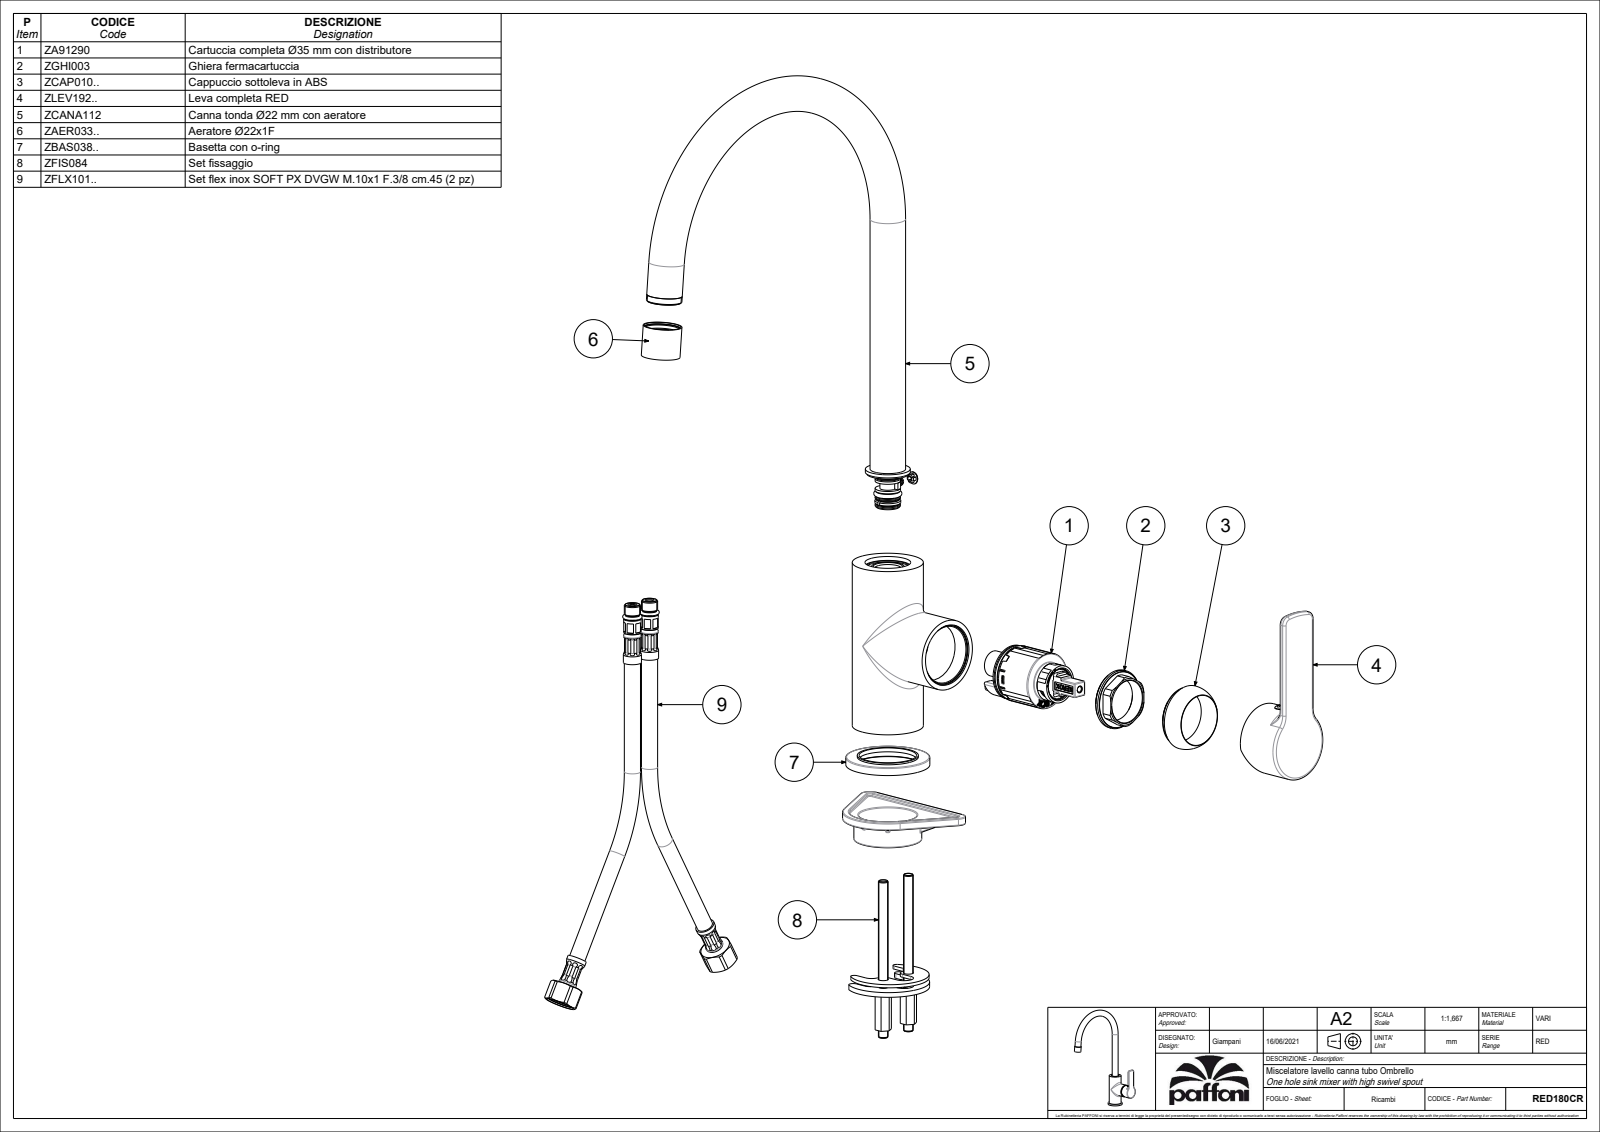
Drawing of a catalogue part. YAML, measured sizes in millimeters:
part_name: "RED180CR"
step_written_by: "CREO PARAMETRIC BY PTC INC, 2020044 (CONFIG_CONTROL_DESIGN)"
units: millimeters
bodies: {solids: 4, faces: 3570, planar: 2541, cylindrical: 604, other: 425}
overall_size: [377.3, 234.97, 111.23]
volume: 223151
surface_area: 146333
round_holes:
  - {diameter: 5.5, count: 3}
  - {diameter: 3, count: 2}
  - {diameter: 4, count: 2}
  - {diameter: 6, count: 2}
  - {diameter: 8, count: 2}
  - {diameter: 9, count: 2}
  - {diameter: 11, count: 2}
  - {diameter: 16, count: 2}
  - {diameter: 17, count: 2}
  - {diameter: 19.6, count: 2}
  - {diameter: 3.3, count: 1}
  - {diameter: 3.4, count: 1}
round_bosses_or_shafts:
  - {diameter: 44, count: 2}
  - {diameter: 22, count: 2}
  - {diameter: 19.5, count: 2}
  - {diameter: 7.6, count: 2}
  - {diameter: 52, count: 1}
  - {diameter: 43, count: 1}
  - {diameter: 42.6, count: 1}
  - {diameter: 37.8, count: 1}
partial_cylinders:
  - {radius: 0.5, count: 103}
  - {radius: 0.3, count: 44}
  - {radius: 0.2, count: 16}
  - {radius: 24.3, count: 12}
  - {radius: 1.5, count: 9}
  - {radius: 1, count: 8}
  - {radius: 1.7, count: 6}
  - {radius: 5, count: 4}
face_to_face_distances: [4.5, 1, 43.3, 3.5, 3.2, 3, 29, 104.5, 47.8, 0.5]
hole_center_spacings: [8.6, 9.6, 13.04, 13.46, 22.61, 62.97, 75.37, 14]
